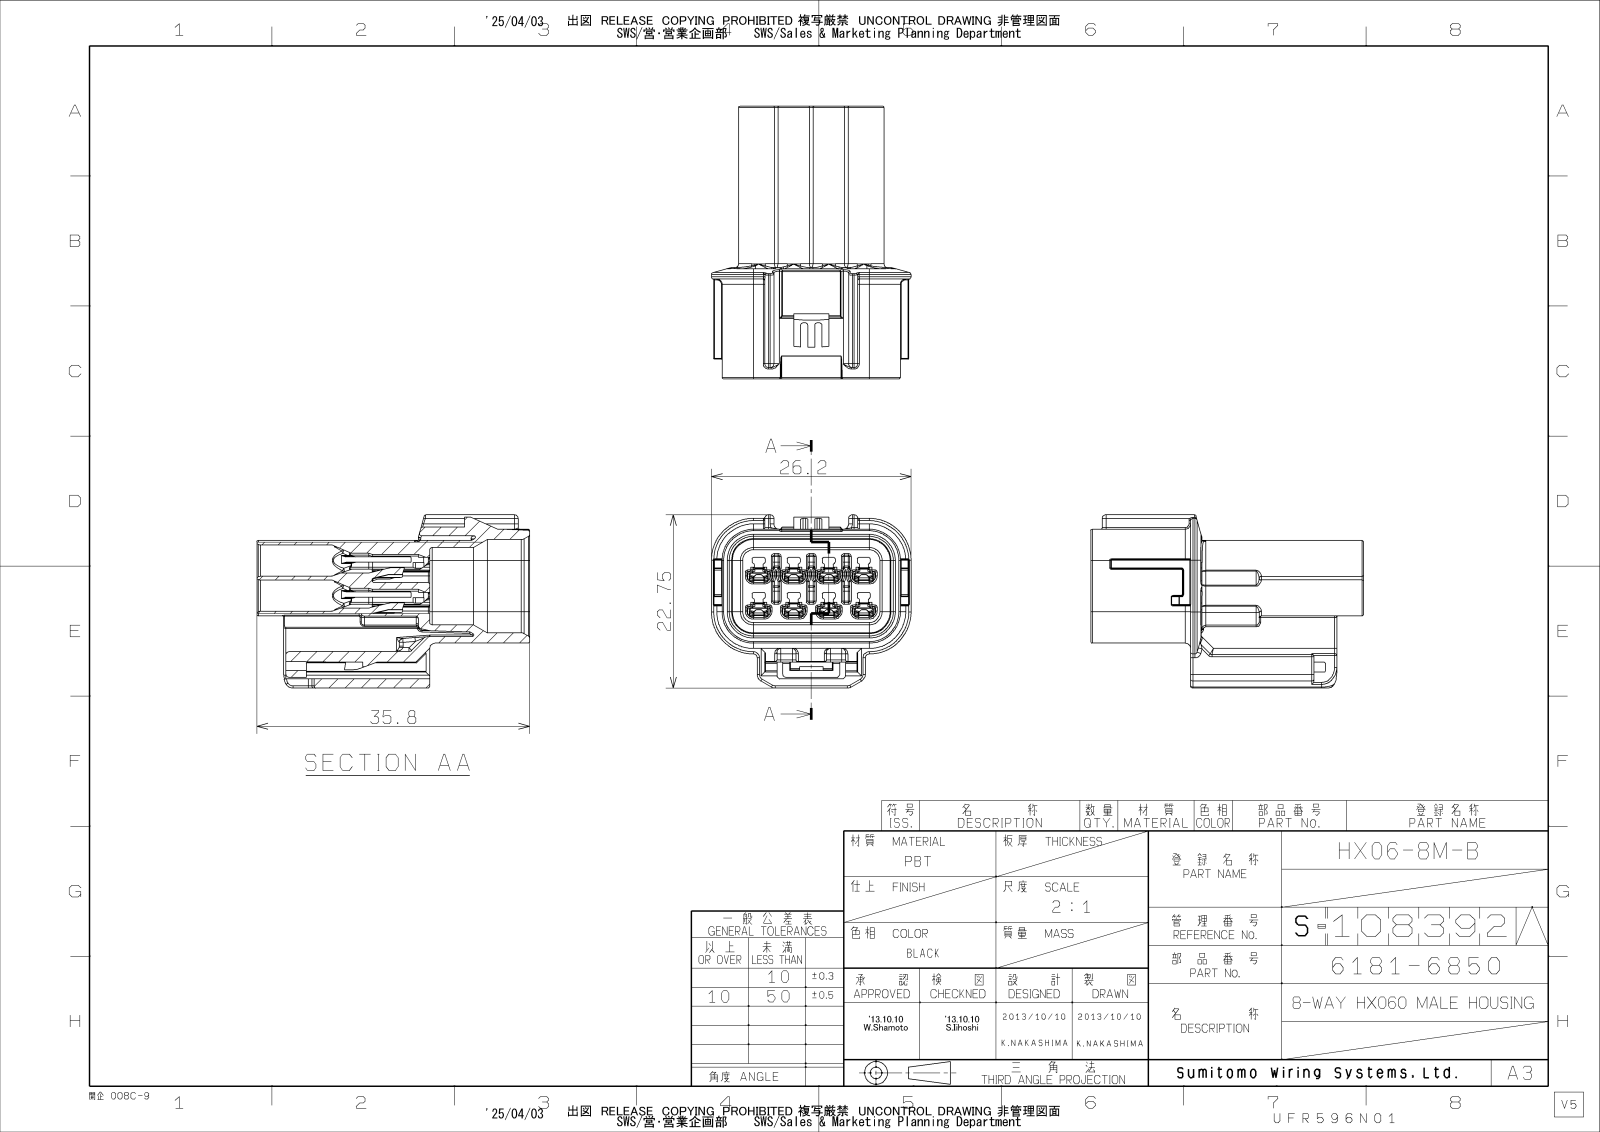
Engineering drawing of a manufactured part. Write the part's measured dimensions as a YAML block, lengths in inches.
part_name: "6181-6850"
step_written_by: "CATIA V5 STEP AP214 v2 (AUTOMOTIVE_DESIGN)"
units: inches
bodies: {solids: 1, faces: 275, planar: 206, cylindrical: 50, other: 19}
overall_size: [1.409, 1.031, 0.896]
volume: 0.422
surface_area: 8.851
round_holes:
  - {diameter: 0.161, count: 8}
partial_cylinders:
  - {radius: 0.104, count: 8}
  - {radius: 0.039, count: 4}
  - {radius: 0.108, count: 4}
  - {radius: 0.161, count: 4}
  - {radius: 0.217, count: 4}
  - {radius: 0.065, count: 2}
  - {radius: 0.079, count: 2}
  - {radius: 0.008, count: 1}
face_to_face_distances: [0.039, 0.094, 0.087, 0.098, 0.244, 0.053, 0.041, 0.047, 0.189, 0.185]
hole_center_spacings: [0.181, 0.256, 0.362, 0.405, 0.543, 0.573]
